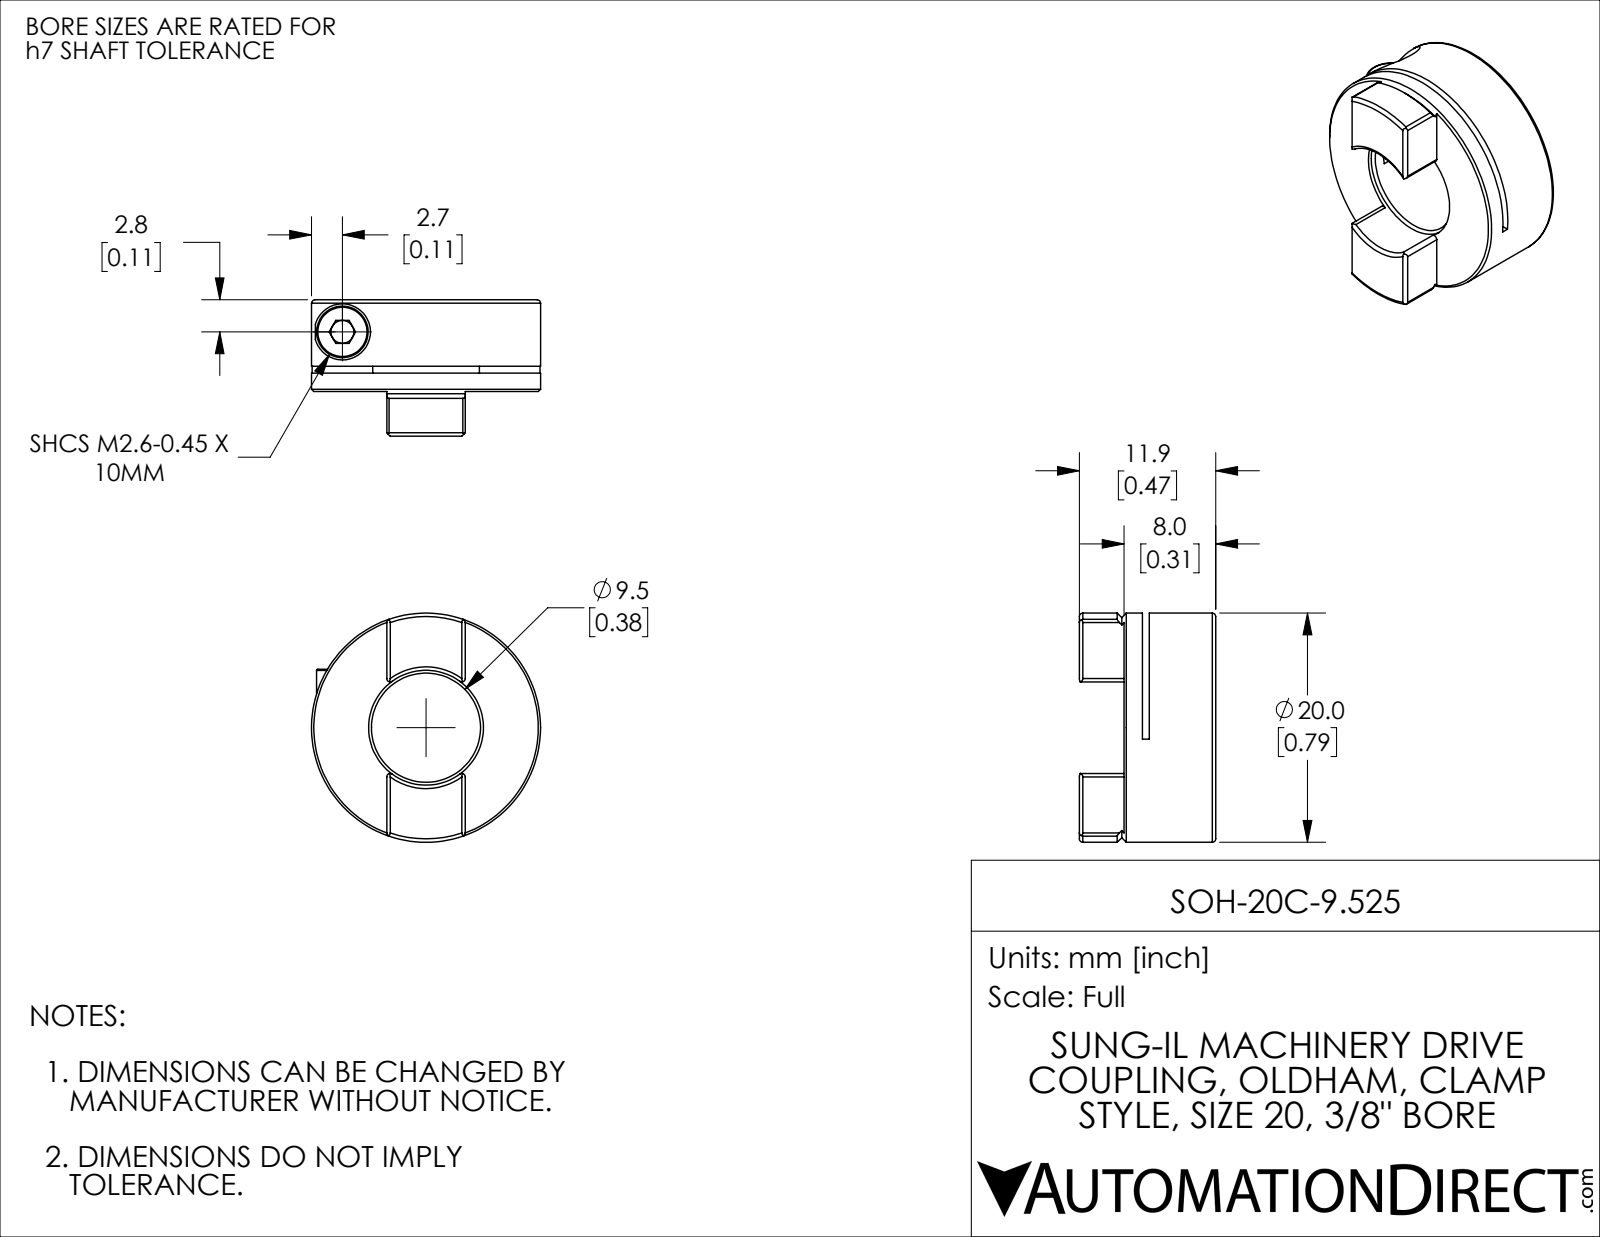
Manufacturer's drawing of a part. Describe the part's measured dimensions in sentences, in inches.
The part is named "SOH-20C-9.525". Its 3-D file was written by "SolidWorks 2021 (CONFIG_CONTROL_DESIGN)". It is 2 solids with 98 faces: 38 planar, 34 cylindrical and 26 other. Overall it measures 0.787 by 0.787 by 0.469 inches. Its volume is 0.126 cubic inches and its surface area 2.978 square inches. Round holes: 1 of diameter 0.079, 1 of diameter 0.081, 1 of diameter 0.11, 1 of diameter 0.193, 1 of diameter 0.375, 1 of diameter 0.395. Round bosses or shafts: 1 of diameter 0.787, 1 of diameter 0.177, 1 of diameter 0.102. Partial cylindrical surfaces (rounded edges, fillets, slot ends): 8 of radius 0.012, 1 of radius 0.886. The main face-to-face distances are 0.315, 0.252, 0.063, 0.228, 0.024, 0.087, 0.24, 0.469, 0.217, 0.154.
